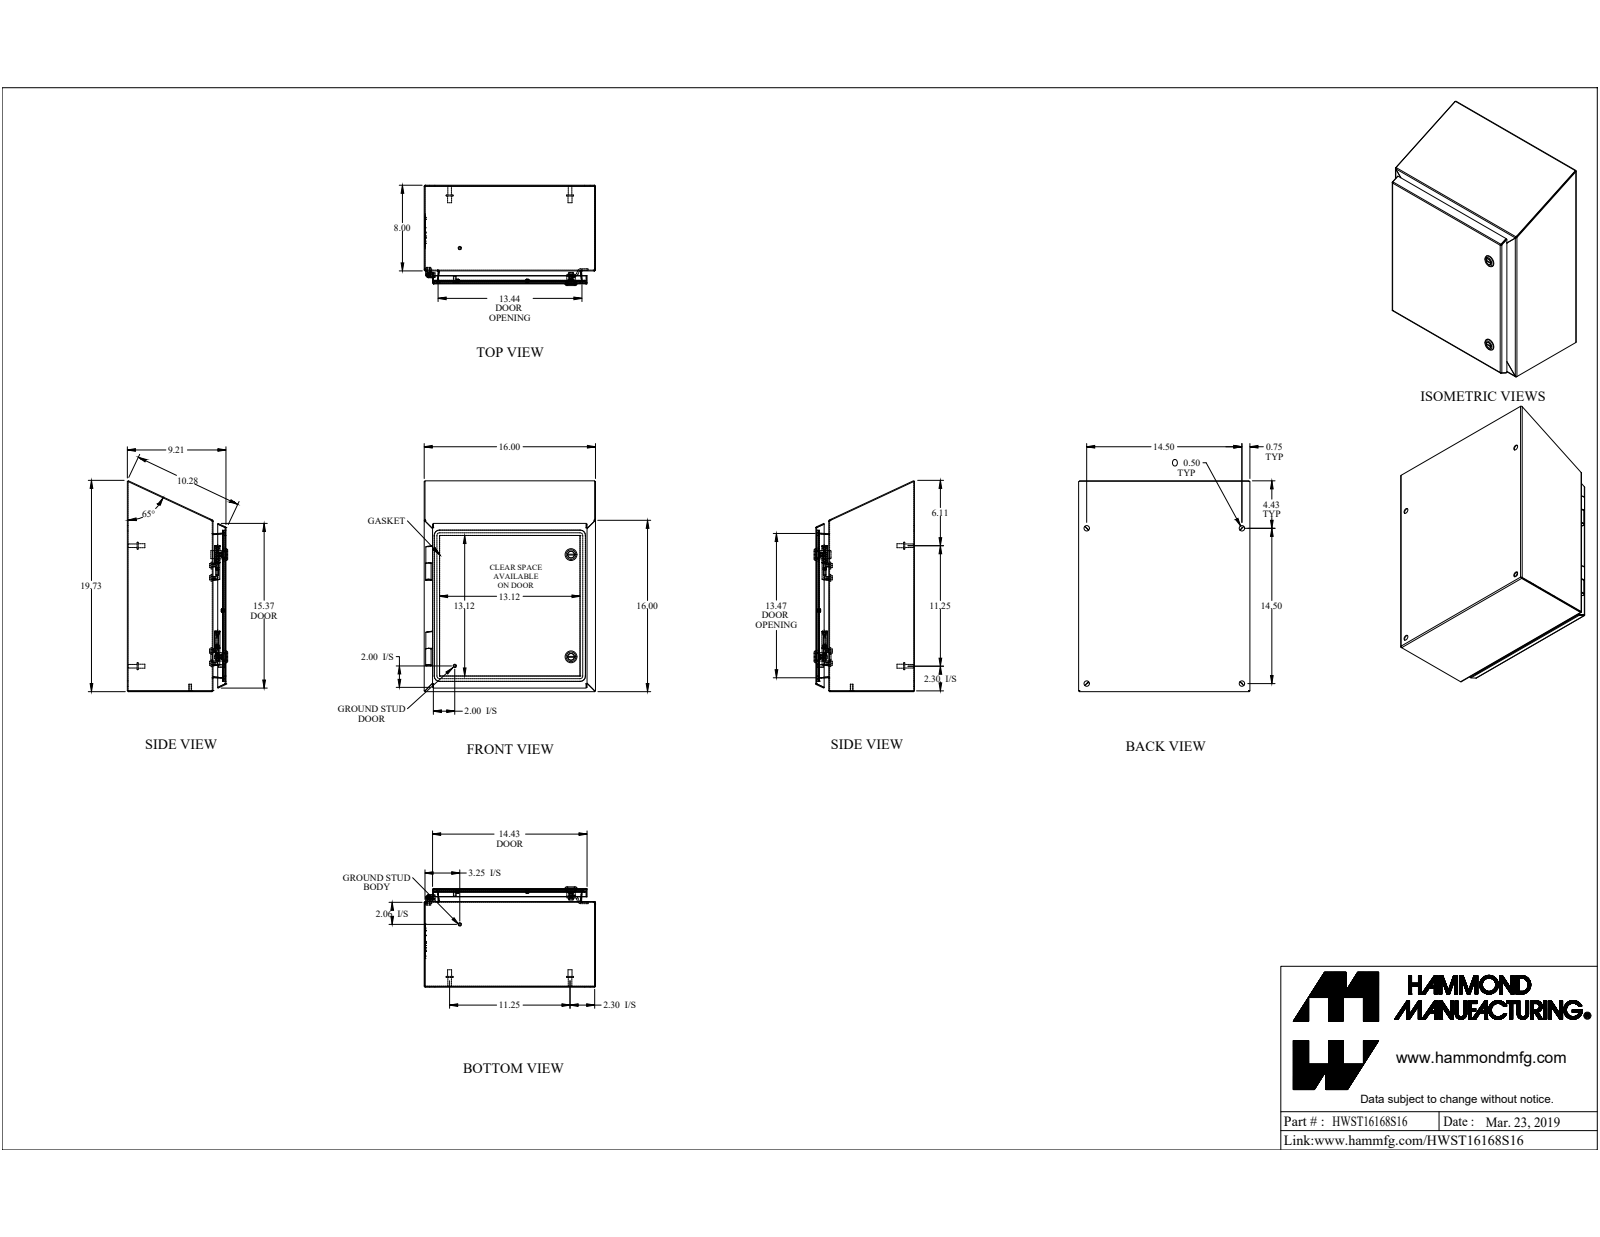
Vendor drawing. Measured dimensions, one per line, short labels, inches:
name: HWST16168SS
written by: SolidWorks 2019 (AUTOMOTIVE_DESIGN)
unit: in
bodies: 43 solids, 1055 faces (649 planar, 292 cylindrical, 114 other)
size: 19.684 × 16 × 9.37
volume: 104.7 in³; area: 2 806 in²
holes: 8× ⌀0.194, 6× ⌀0.5, 4× ⌀0.24, 4× ⌀0.275, 2× ⌀0.13, 2× ⌀0.197, 2× ⌀0.387, 2× ⌀0.63, 2× ⌀0.768, 1× ⌀0.24, 1× ⌀3.5
bosses: 8× ⌀0.226, 6× ⌀0.625, 4× ⌀0.65, 4× ⌀0.375, 4× ⌀0.332, 4× ⌀0.25, 3× ⌀0.236, 2× ⌀1.1
rounds: 24× R0.25, 16× R0.039, 16× R0.108, 12× R0.012, 12× R0.036, 12× R0.125, 9× R0.108, 7× R0.036
face distances: 0.072, 15.928, 9.066, 9.138, 0.072, 9.138, 9.21, 15.856, 7.928, 16
hole spacings: 1.142, 7.979, 14.5, 6.837, 7.98, 9.12, 20.506, 1.141
